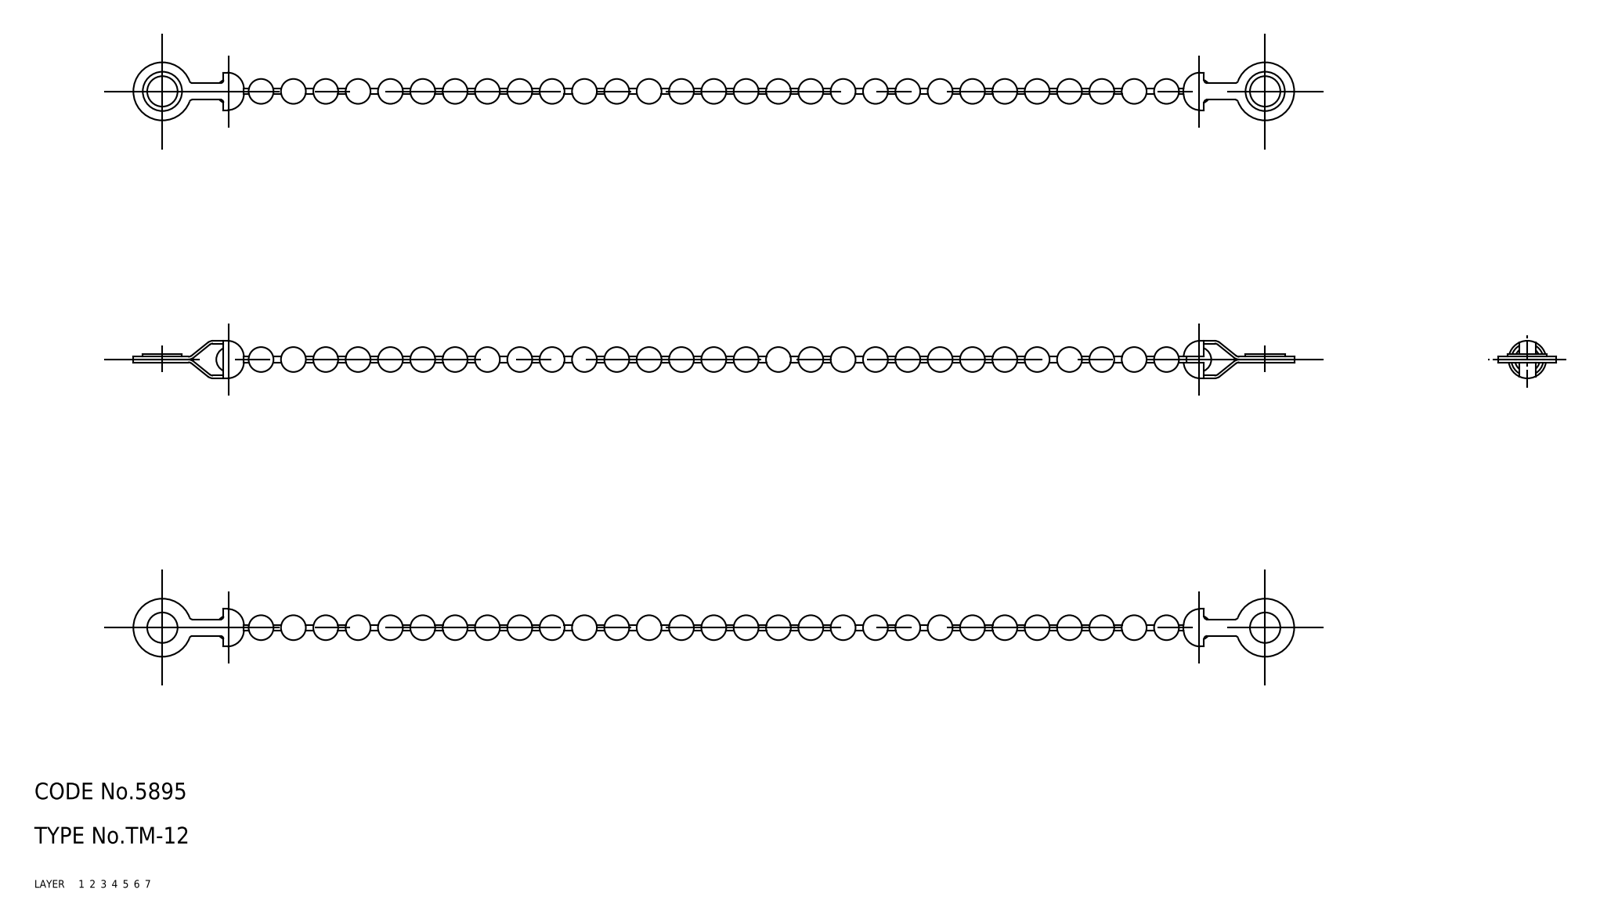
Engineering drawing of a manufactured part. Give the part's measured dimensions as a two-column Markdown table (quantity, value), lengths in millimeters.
| quantity | value |
| --- | --- |
| part name | 67122199; 67122212; 67122225; 67122238 (+8 more) |
| STEP written by | CADfix (AUTOMOTIVE_DESIGN) |
| units | millimeters |
| bodies | 38 solids, 195 faces (0 planar, 0 cylindrical, 195 other) |
| overall size | 233.4 × 10.5 × 6.8 |
| volume | 1 893 mm³ |
| surface area | 4 218 mm² |
